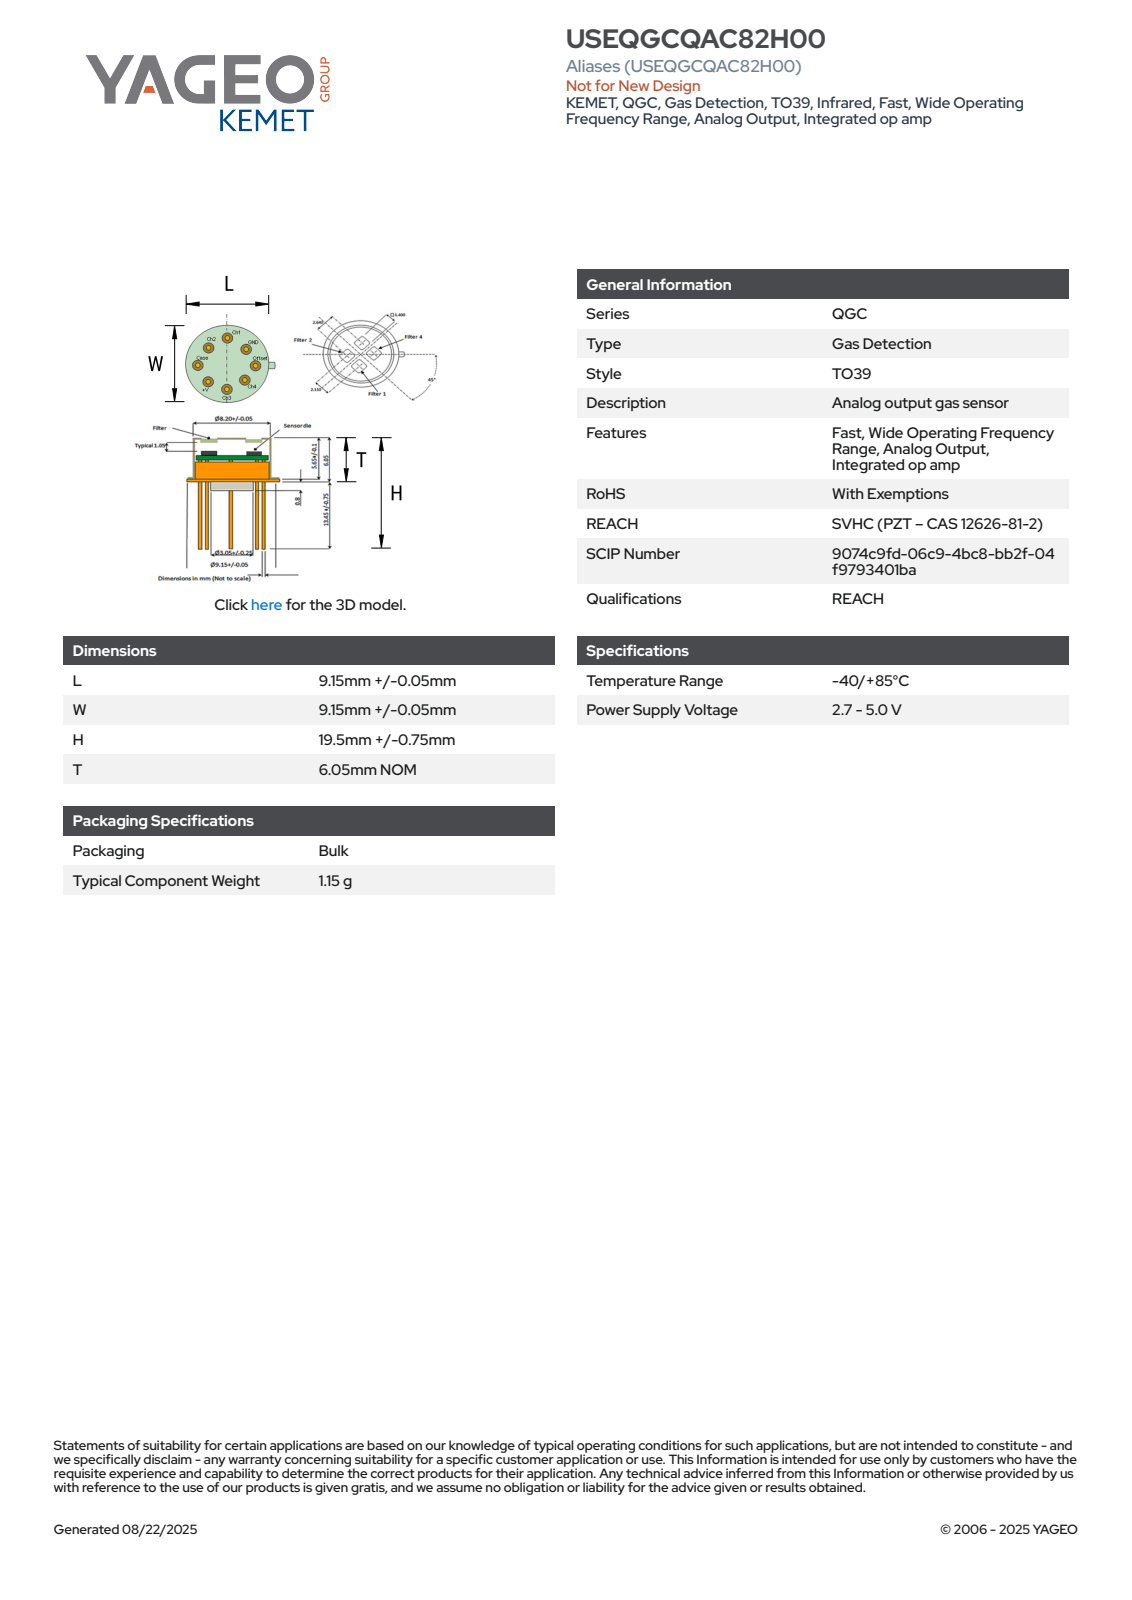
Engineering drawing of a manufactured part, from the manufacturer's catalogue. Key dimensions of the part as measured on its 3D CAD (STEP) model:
Part name (STEP PRODUCT): SF_QGCQ_L9.2W9.2H20.25T6.05
STEP written by: SolidWorks 2014 (AUTOMOTIVE_DESIGN)
Units: millimetres
Bodies: 1 solid, 114 faces (90 planar, 24 cylindrical, 0 other)
Overall size (bounding box): 20.25 × 9.68 × 9.19
Volume: 354 mm³ · Surface area: 471 mm²
Round bosses / shafts (diameter × count): ⌀0.48 ×8, ⌀9.19 ×1, ⌀8.25 ×1, ⌀3.05 ×1
Main face-to-face distances: 6.05, 5.75, 0.8, 1.1, 6.85, 13.4, 14.2, 14.5, 20.25, 0.44
